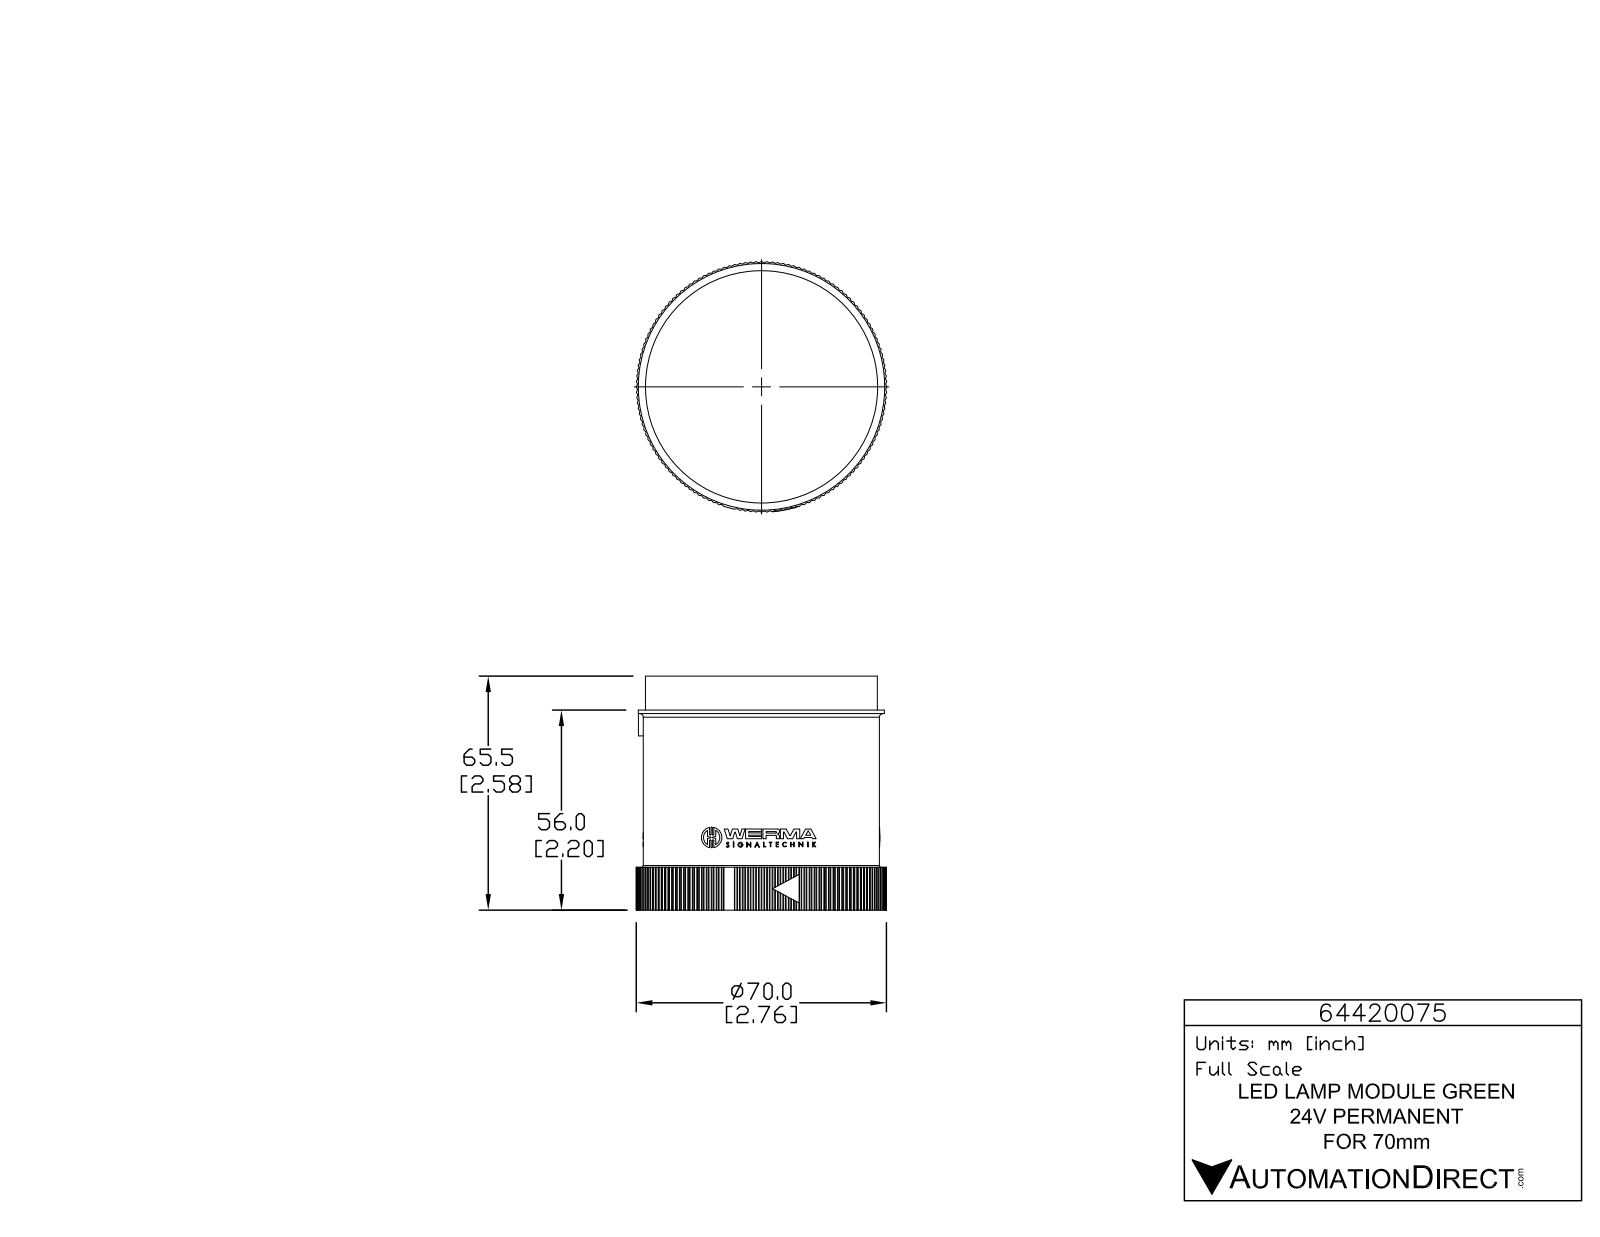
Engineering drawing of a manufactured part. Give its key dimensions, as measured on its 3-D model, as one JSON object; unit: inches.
{"part_name": "64420075", "step_written_by": "SolidWorks 2015 (AUTOMOTIVE_DESIGN)", "units": "inches", "bodies": {"solids": 1, "faces": 1400, "planar": 832, "cylindrical": 563, "other": 5}, "overall_size": [2.762, 2.762, 2.579], "volume_in3": 12.02, "surface_area_in2": 37.48, "round_holes": [[0.039, 3], [2.575, 1]], "round_bosses_or_shafts": [[0.226, 3], [0.056, 3], [2.717, 1], [2.606, 1], [2.559, 1]], "partial_cylinders_radius": [[0.008, 285], [0.008, 6], [0.008, 6], [0.008, 6], [0.131, 6], [0.004, 3], [0.005, 3], [0.008, 3]], "face_to_face_distances": [2.201, 2.451, 0.378, 2.579, 2.205, 1.827, 0.374, 2.452, 0.472, 0.094]}
